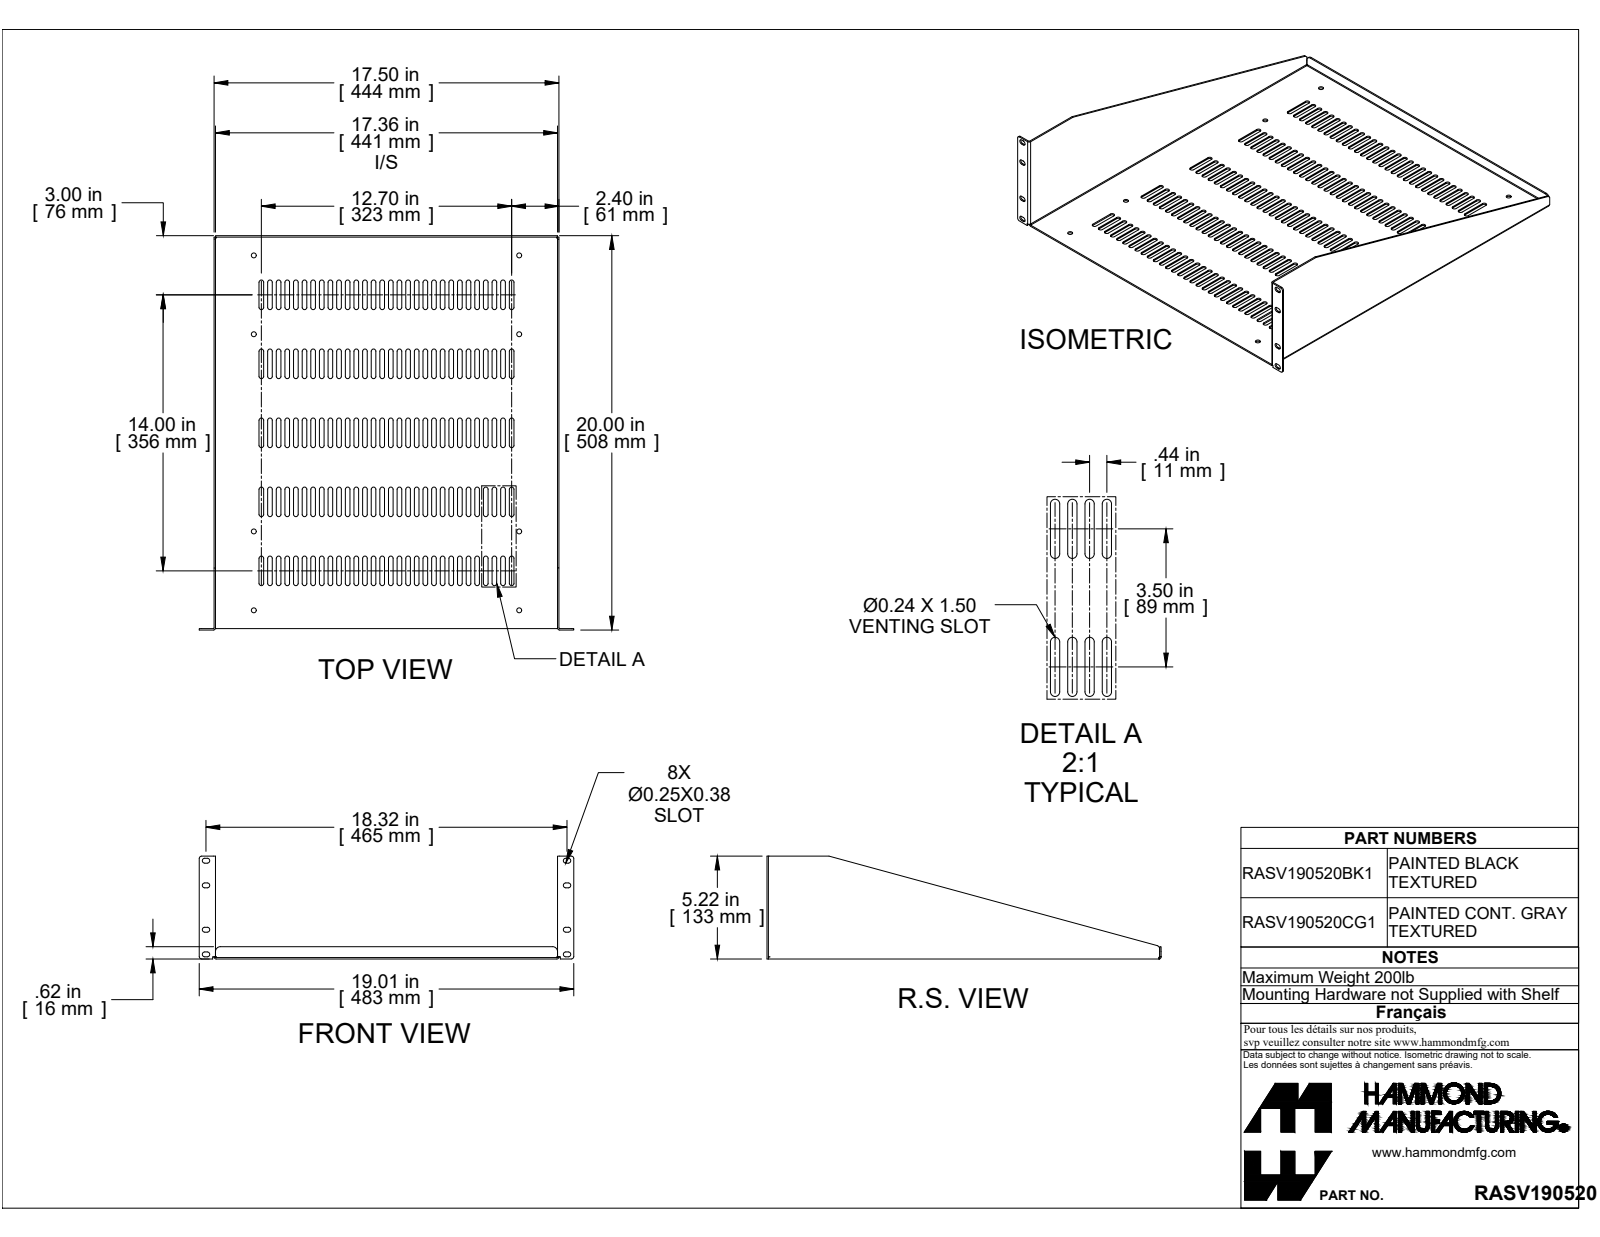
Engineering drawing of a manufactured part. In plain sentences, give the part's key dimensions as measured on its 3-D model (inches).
The part is named "RASV190520BK1". Its 3-D file was written by "SolidWorks 2019 (CONFIG_CONTROL_DESIGN)". It is 1 solid with 704 faces: 356 planar, 344 cylindrical and 4 other. Overall it measures 20 by 19.006 by 5.218 inches. Its volume is 31.7 cubic inches and its surface area 923.5 square inches. Round holes: 8 of diameter 0.25. Partial cylindrical surfaces (rounded edges, fillets, slot ends): 290 of radius 0.118, 20 of radius 0.125, 10 of radius 0.117, 5 of radius 0.036, 5 of radius 0.108, 3 of radius 0.055, 2 of radius 0.25. The main face-to-face distances are 0.072, 17.428, 17.356, 17.5, 19.856, 19.928, 0.072, 19.928, 20, 0.876. The hole center spacings are 4, 13.468, 14, 14.049, 19.426, 10, 16.774, 18.
